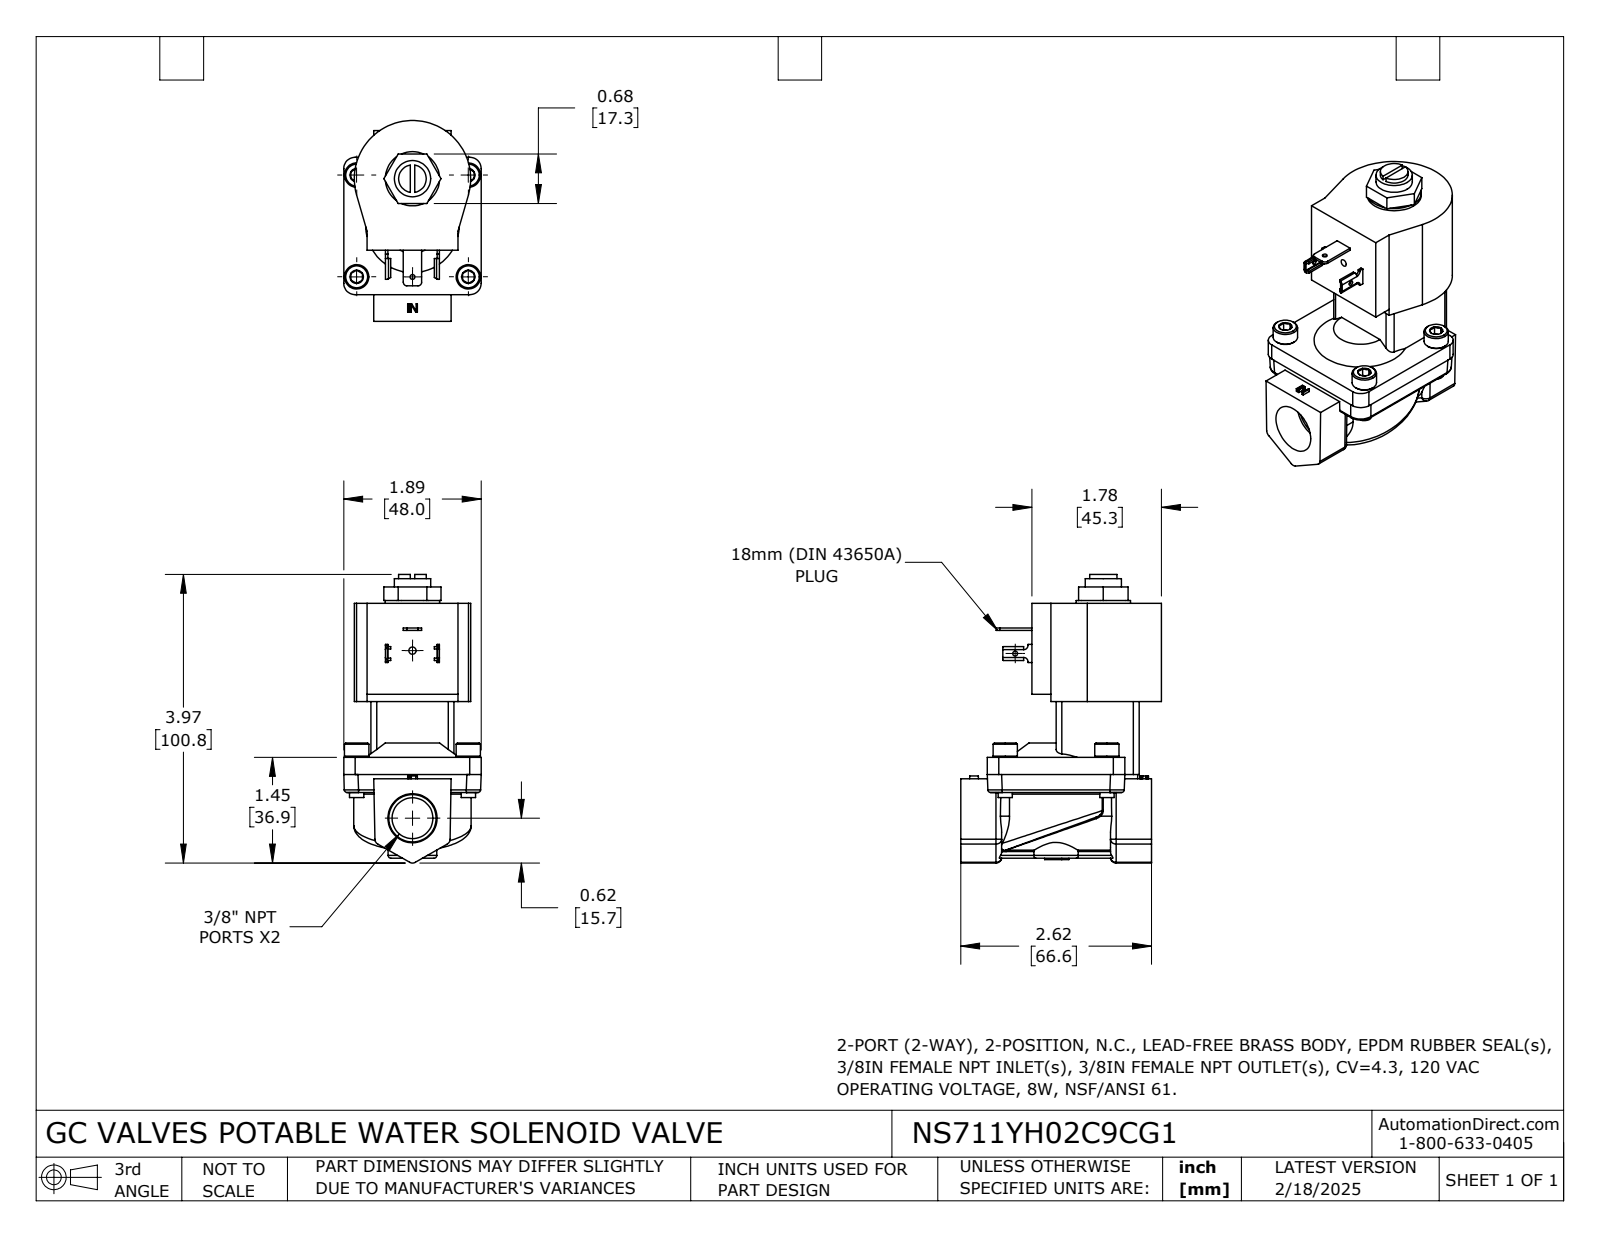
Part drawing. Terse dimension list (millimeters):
name: NS711YH02C9CG1
written by: SolidWorks 2024 (CONFIG_CONTROL_DESIGN)
unit: mm
bodies: 1 solid, 486 faces (270 planar, 113 cylindrical, 103 other)
size: 100.77 × 70.12 × 48
volume: 134 803 mm³; area: 25 680 mm²
holes: 1× ⌀1.68, 1× ⌀1.7, 1× ⌀2.53, 1× ⌀14.27, 1× ⌀30.48
bosses: 4× ⌀8.5, 4× ⌀5, 1× ⌀18.95, 1× ⌀12.67, 1× ⌀9.65
rounds: 15× R2, 6× R0.5, 6× R1, 4× R0.15, 4× R1.04, 4× R4, 4× R5, 2× R1.27
face distances: 19.5, 34.29, 53.79, 29, 22.04, 2.54, 31.75, 33.3, 37.44, 9.5
hole spacings: 34.29, 58.5
